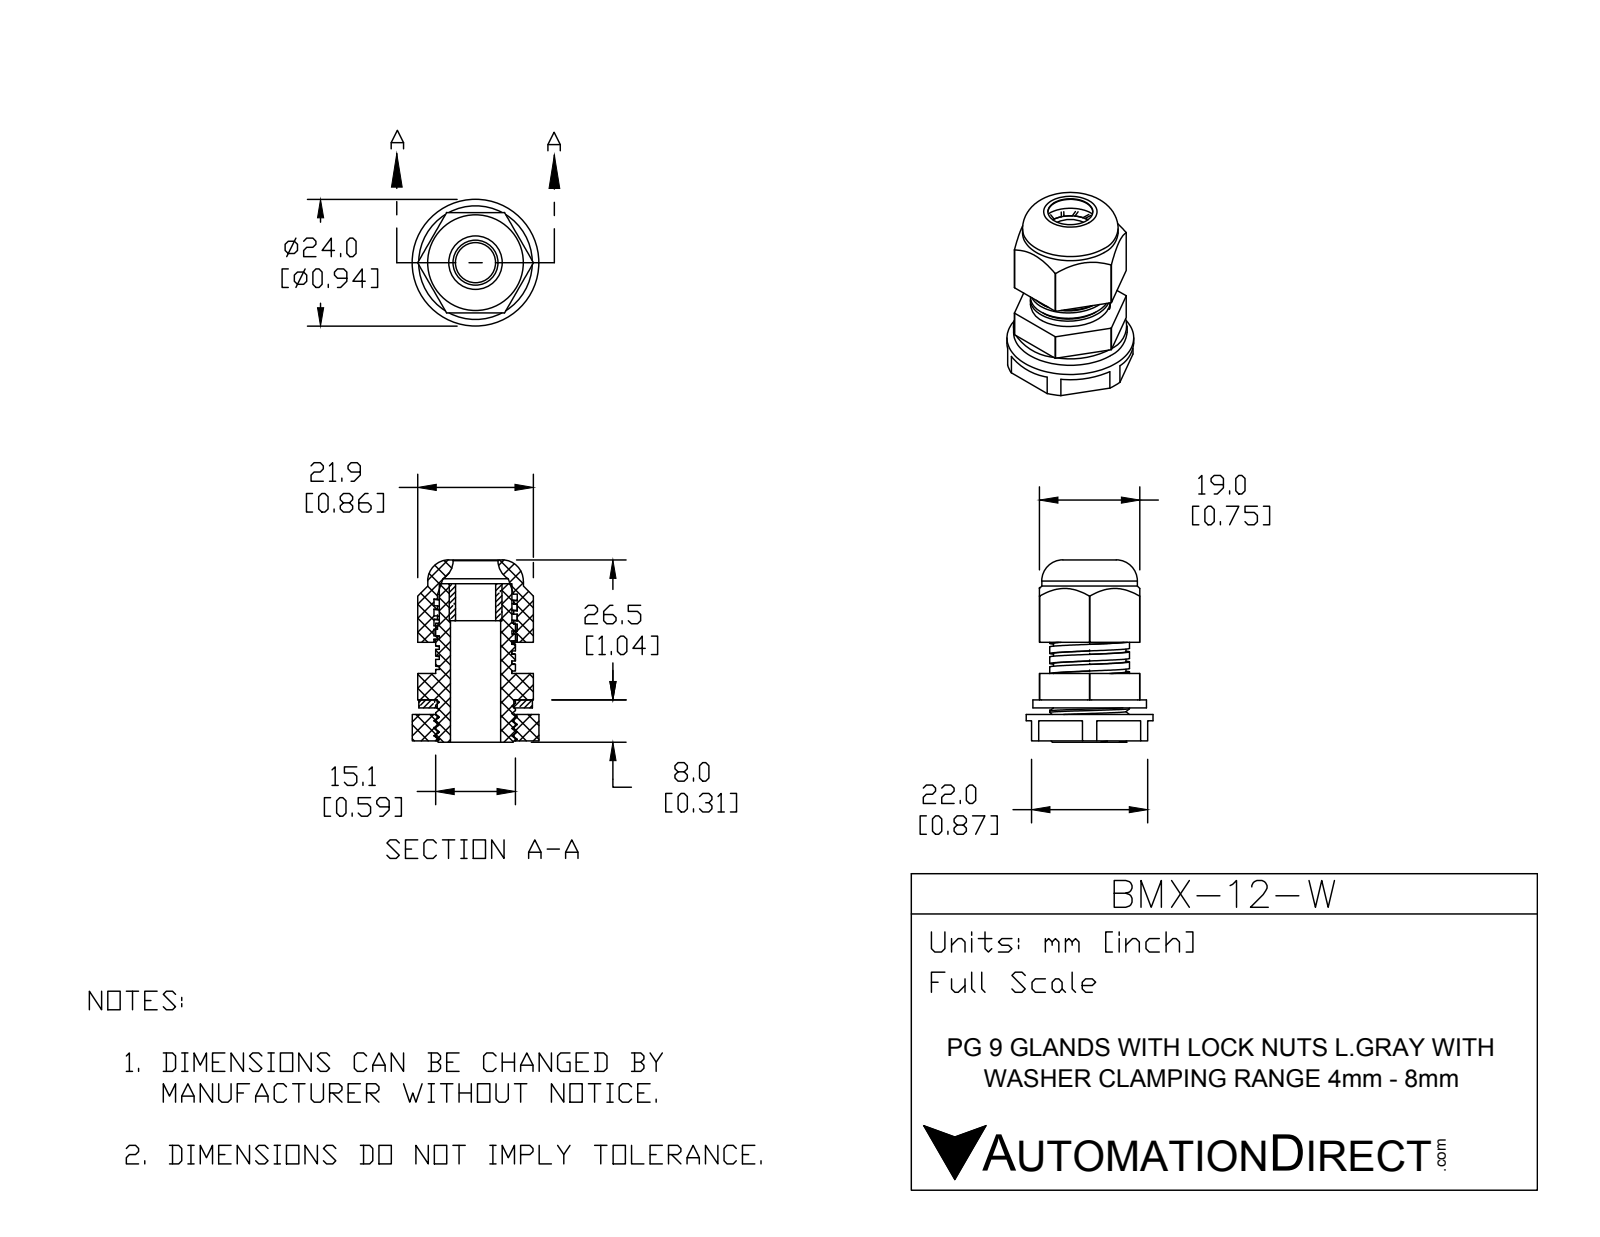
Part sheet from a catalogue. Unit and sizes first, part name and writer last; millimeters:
Units: millimetres
Overall size (bounding box): 34.5 × 24 × 24
Round holes (diameter × count): ⌀7.6 ×1, ⌀8.5 ×1, ⌀9.5 ×1, ⌀10 ×1, ⌀14.43 ×1, ⌀14.5 ×1
Round bosses / shafts (diameter × count): ⌀24 ×1, ⌀21.5 ×1, ⌀18.1 ×1, ⌀15.1 ×1, ⌀13.75 ×1
Partial cylindrical surfaces — rounded edges, fillets, slot ends (radius × count): R10.95 ×1
Main face-to-face distances: 19, 1.5, 5, 7.75, 2.75, 6.5, 20.5, 0.5, 22, 6.25
Volume: 7 153 mm³ · Surface area: 8 076 mm²
Bodies: 5 solids, 197 faces (99 planar, 75 cylindrical, 23 other)
Part name (STEP PRODUCT): BMX-12-W
STEP written by: SolidWorks 2015 (CONFIG_CONTROL_DESIGN)
